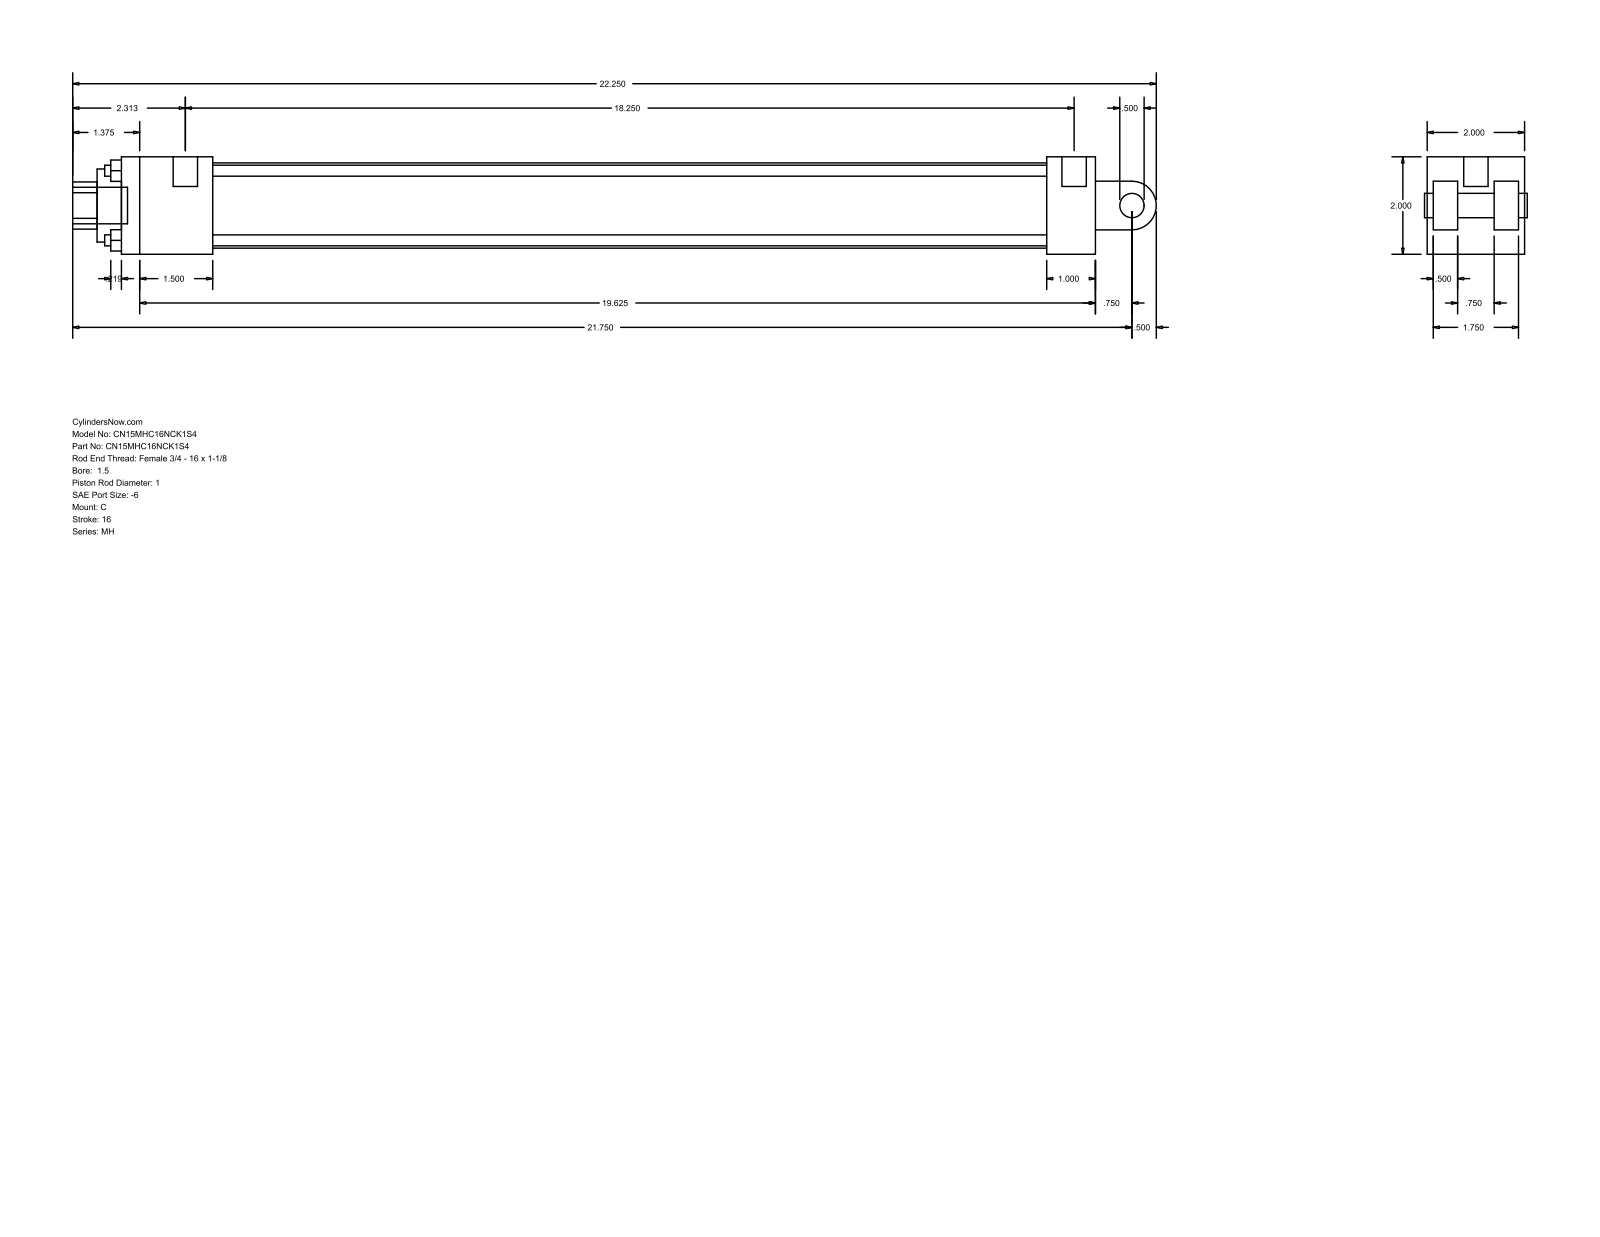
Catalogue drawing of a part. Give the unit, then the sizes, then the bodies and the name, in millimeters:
Units: millimetres
Overall size (bounding box): 565.15 × 50.8 × 50.8
Round holes (diameter × count): ⌀5.71 ×4, ⌀5.56 ×2, ⌀12.7 ×1, ⌀25.4 ×1, ⌀38.1 ×1, ⌀44.45 ×1
Round bosses / shafts (diameter × count): ⌀12.7 ×2, ⌀5.56 ×2, ⌀19.05 ×1
Partial cylindrical surfaces — rounded edges, fillets, slot ends (radius × count): R12.29 ×1, R12.7 ×1
Main face-to-face distances: 50.8, 12.7, 47.63, 3.17, 15.87, 25.4, 34.93, 31.76, 508, 38.1
Hole centre spacings: 25.68, 36.32, 51.36
Bodies: 0 solids, 99 faces (70 planar, 29 cylindrical, 0 other)
Part name (STEP PRODUCT): MH_C__0150_1
STEP written by: GSSL Pune (CONFIG_CONTROL_DESIGN)
